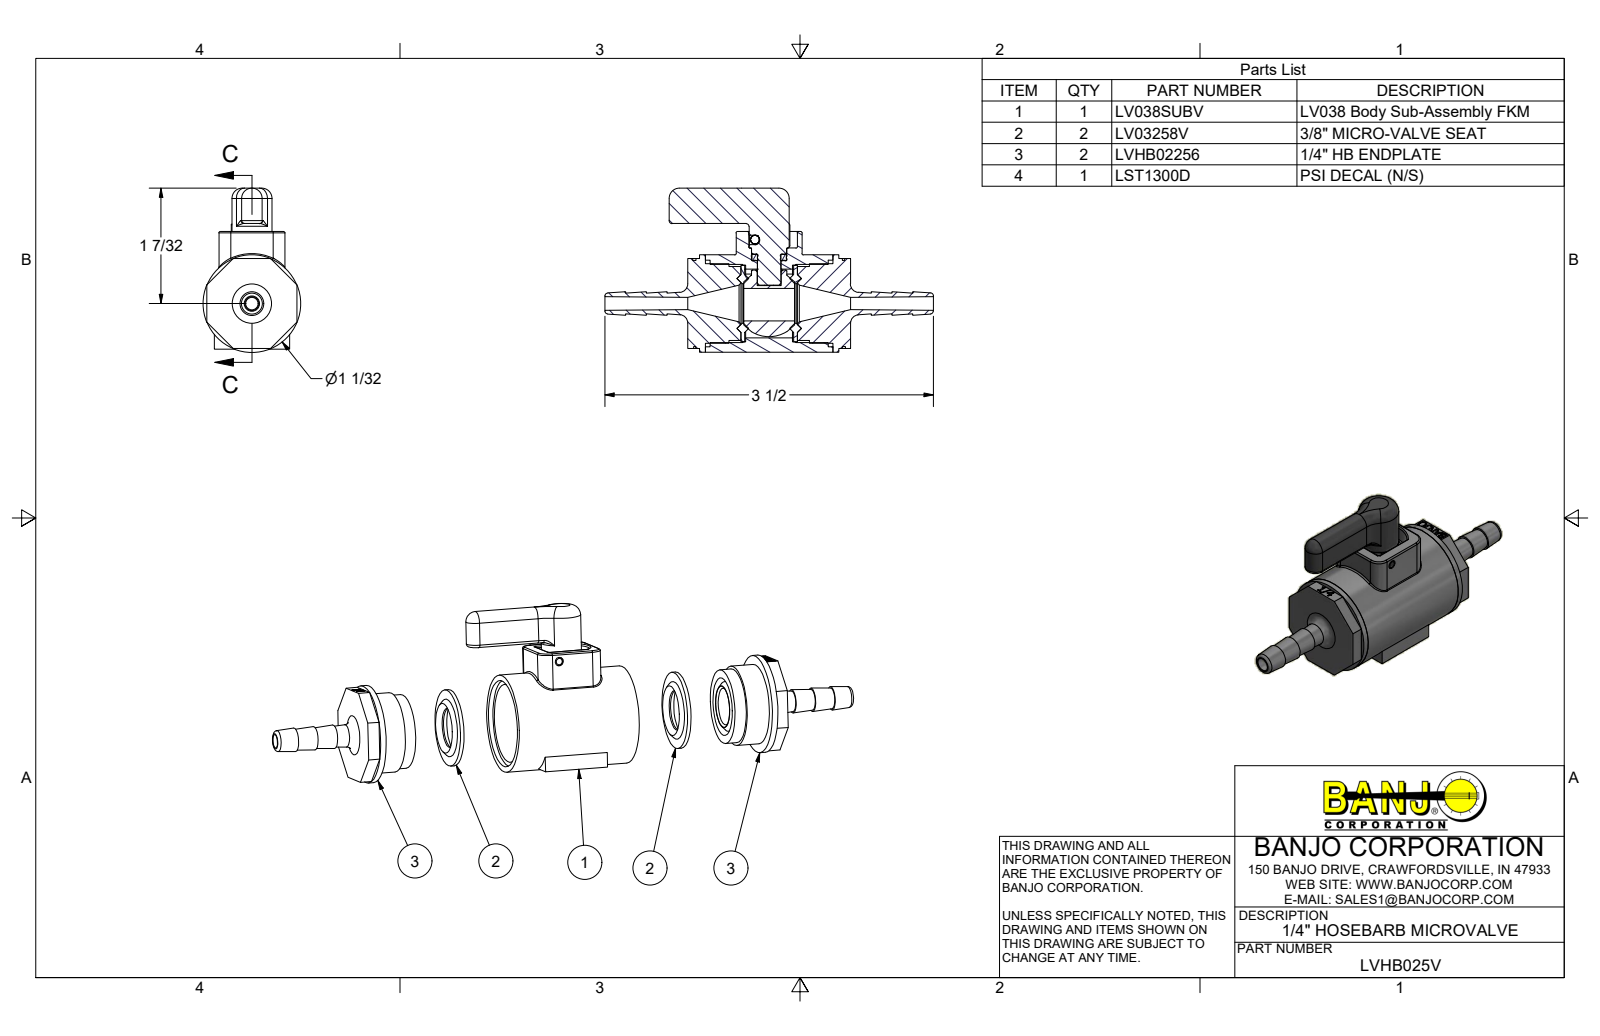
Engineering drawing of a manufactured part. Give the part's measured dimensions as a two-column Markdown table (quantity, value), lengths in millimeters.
| quantity | value |
| --- | --- |
| part name | LVHB025V; LV038SUBV; LV03254A; AQ010V (+5 more) |
| STEP written by | Autodesk Inventor 2012 (AUTOMOTIVE_DESIGN) |
| units | millimeters |
| bodies | 9 solids, 643 faces (310 planar, 101 cylindrical, 232 other) |
| overall size | 88.6 × 44.3 × 26.3 |
| volume | 25 580 mm³ |
| surface area | 17 160 mm² |
| round holes (diameter × count) | 2.4 × 1, 6.4 × 1, 9.3 × 1, 9.4 × 1, 9.6 × 1, 10.7 × 1, 18.5 × 1, 20.7 × 1, 21.1 × 1, 23.4 × 1 |
| round bosses / shafts (diameter × count) | 26.3 × 1, 21.5 × 1, 20.6 × 1, 19.9 × 1, 10.8 × 1, 9.5 × 1, 9.4 × 1, 6.4 × 1 |
| partial cylindrical surfaces (radius × count) | 0.3 × 16, 0.4 × 14, 3.2 × 4, 0.8 × 2, 1.3 × 2, 2.8 × 2, 6.4 × 2, 1.2 × 1 |
| main face-to-face distances | 24.8, 4.8, 39.2, 14.4, 29.6, 9.6, 1.3, 43.9, 8.3, 34.4 |
